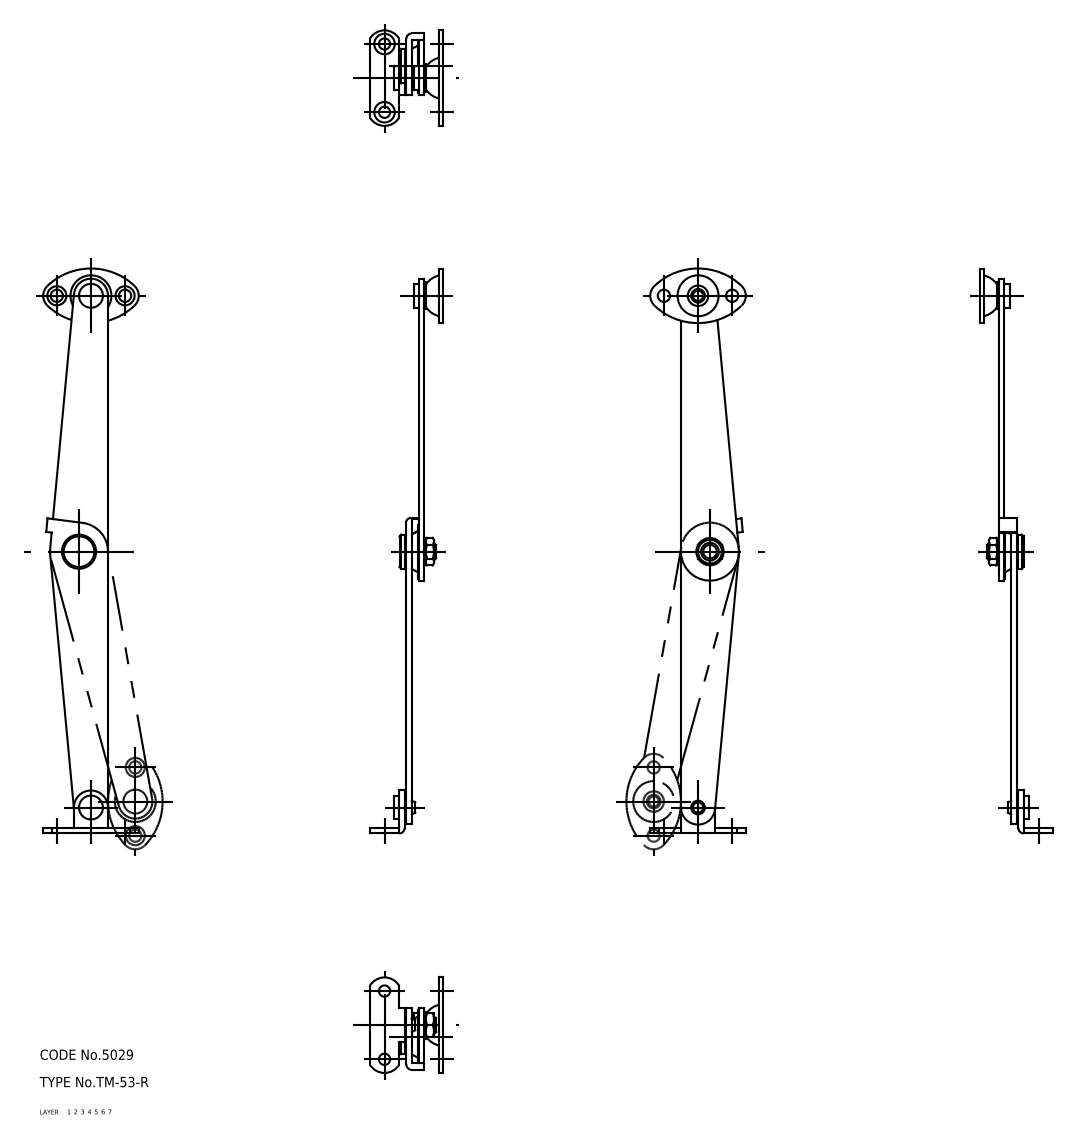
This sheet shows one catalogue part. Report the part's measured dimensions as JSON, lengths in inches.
{"part_name": "rivet_A; rivet_B; washer_2; washer_3 (+7 more)", "step_written_by": "CADfix (AUTOMOTIVE_DESIGN)", "units": "inches", "bodies": {"solids": 12, "faces": 142, "planar": 0, "cylindrical": 0, "other": 142}, "overall_size": [6.52, 1.102, 0.819], "volume_in3": 0.325, "surface_area_in2": 13.23}
